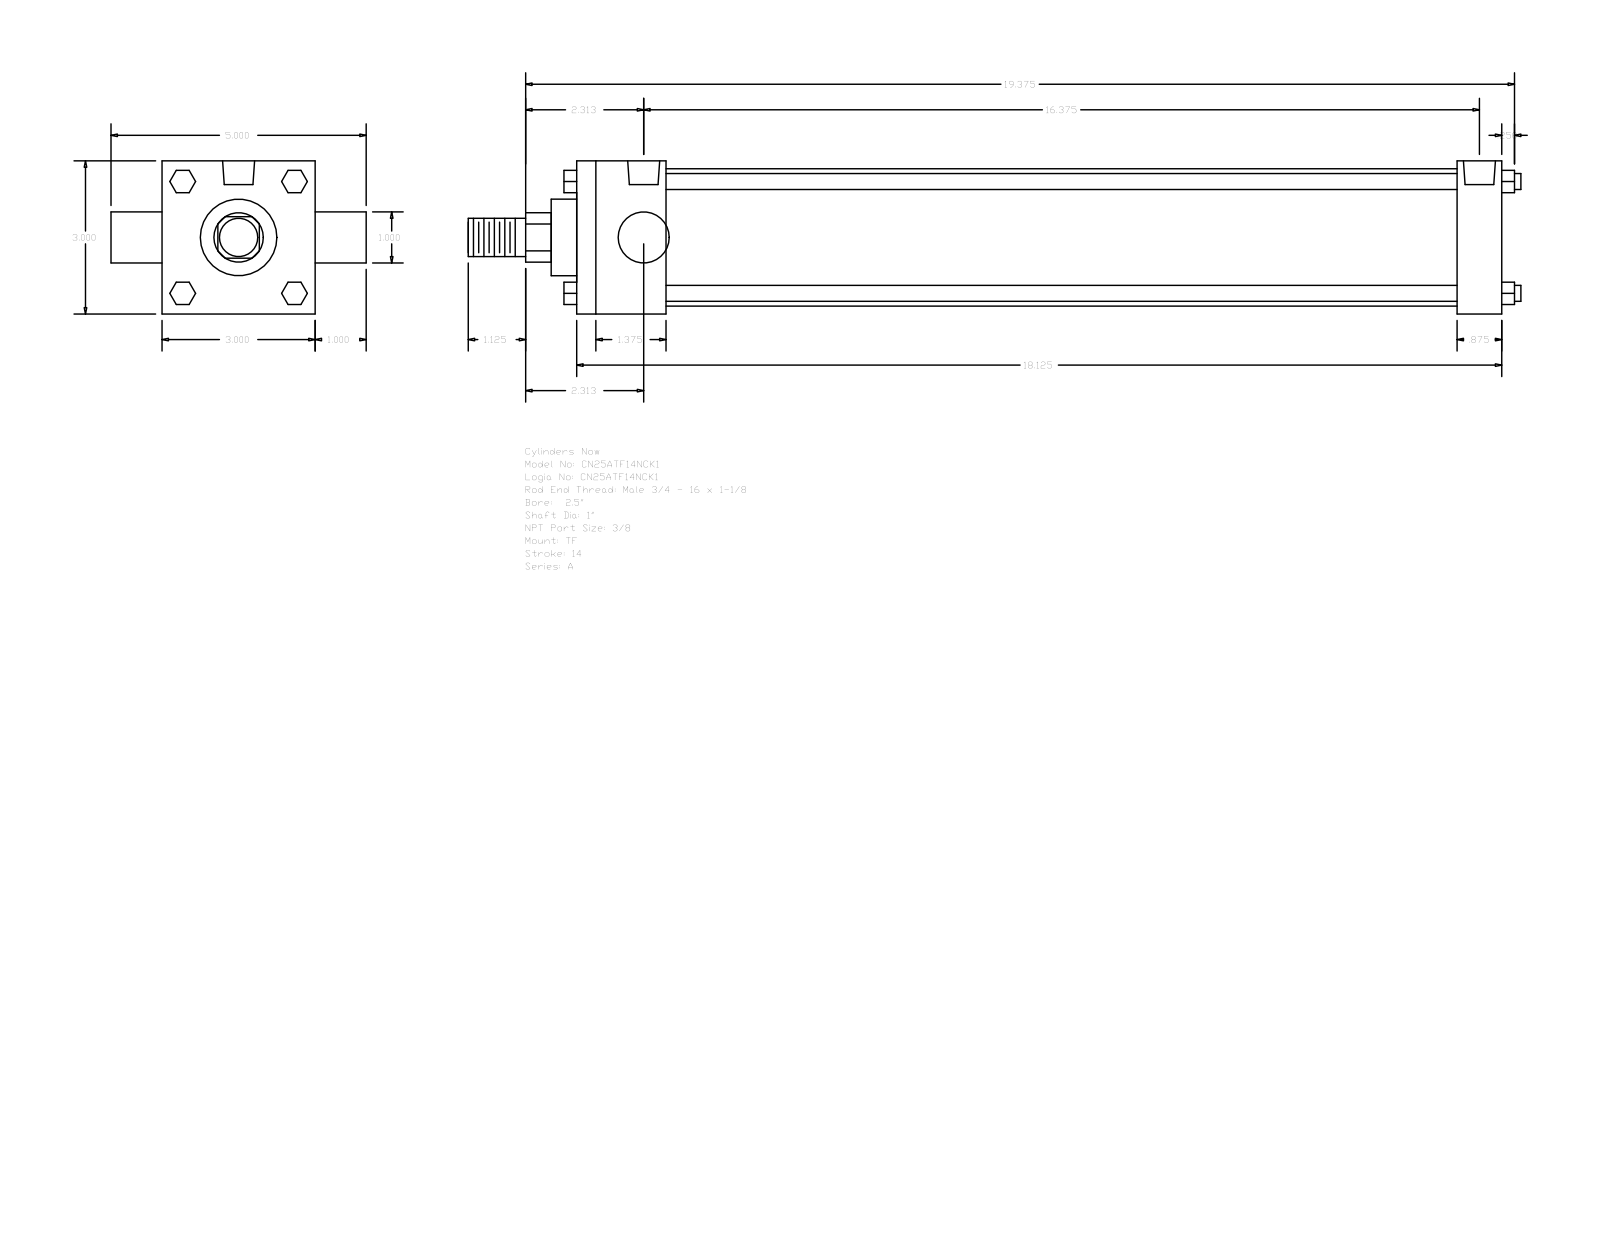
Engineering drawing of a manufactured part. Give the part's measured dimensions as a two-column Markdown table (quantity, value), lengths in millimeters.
| quantity | value |
| --- | --- |
| part name | A_TF__0250_1 |
| STEP written by | GSSL Pune (CONFIG_CONTROL_DESIGN) |
| units | millimeters |
| bodies | 0 solids, 120 faces (92 planar, 28 cylindrical, 0 other) |
| overall size | 523.88 × 127 × 76.2 |
| round holes (diameter × count) | 5.56 × 3, 15.93 × 2 |
| round bosses / shafts (diameter × count) | 7.94 × 4, 25.4 × 2, 68.33 × 1, 38.1 × 1, 19.05 × 1 |
| partial cylindrical surfaces (radius × count) | 12.29 × 1 |
| main face-to-face distances | 76.2, 460.37, 44.45, 438.15, 393.7, 415.92, 22.22, 25.4, 101.6, 473.07 |
| hole center spacings | 2.38, 418.3, 415.92, 420.68 |
